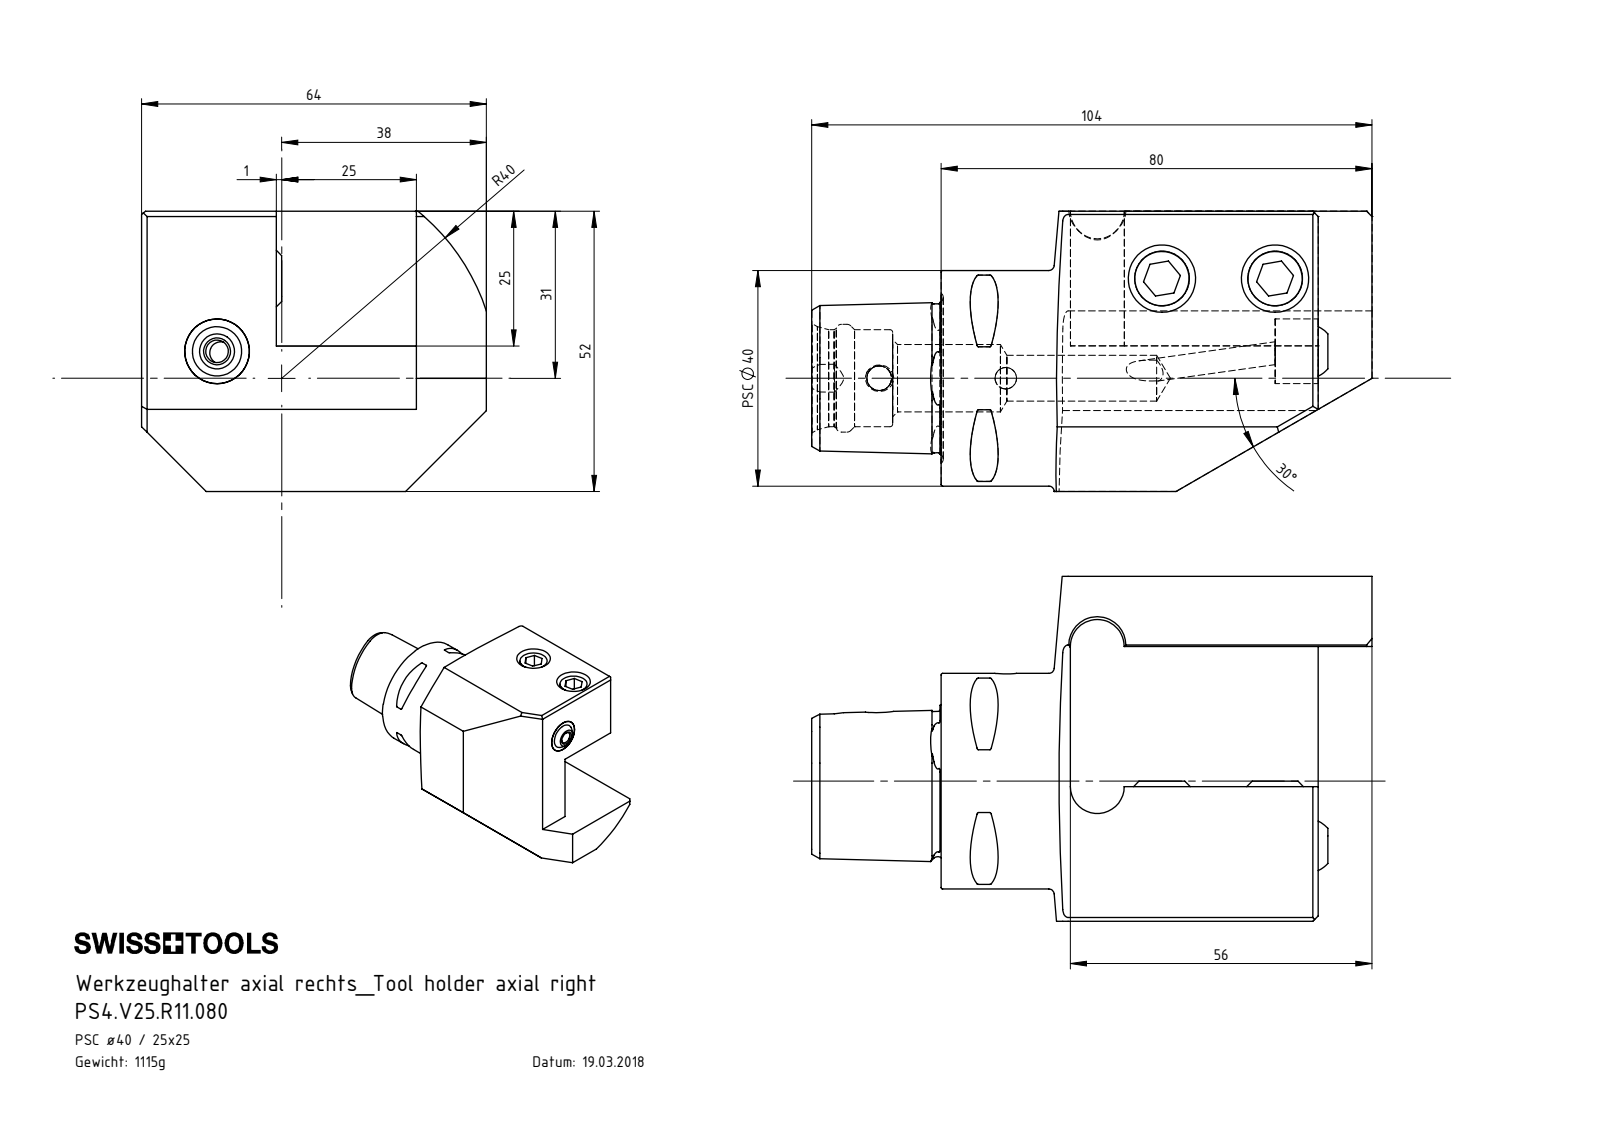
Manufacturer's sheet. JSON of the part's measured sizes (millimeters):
{"part_name": "KU1-U12.001.010; KU1-U12.001.010_1; ISO 4026 - M12 x 25; PS4.V25.R11.080 (+2 more)", "step_written_by": "SolidWorks 2017 (AUTOMOTIVE_DESIGN)", "units": "millimeters", "bodies": {"solids": 5, "faces": 158, "planar": 58, "cylindrical": 31, "other": 69}, "overall_size": [104, 64, 52], "volume_mm3": 142415, "surface_area_mm2": 31142, "round_holes": [[4.2, 2], [10.2, 2], [4, 1], [4.6, 1], [7, 1], [8.5, 1], [12, 1], [12.5, 1], [18, 1], [20, 1]], "round_bosses_or_shafts": [[12, 2], [40, 1]], "partial_cylinders_radius": [[0.3, 8], [5, 2], [3, 1], [40, 1]], "face_to_face_distances": [25, 51, 13, 64, 26, 52, 27, 39, 24, 46], "hole_center_spacings": [13, 21, 23.5, 34.4, 53.31, 55.66, 75.79]}
